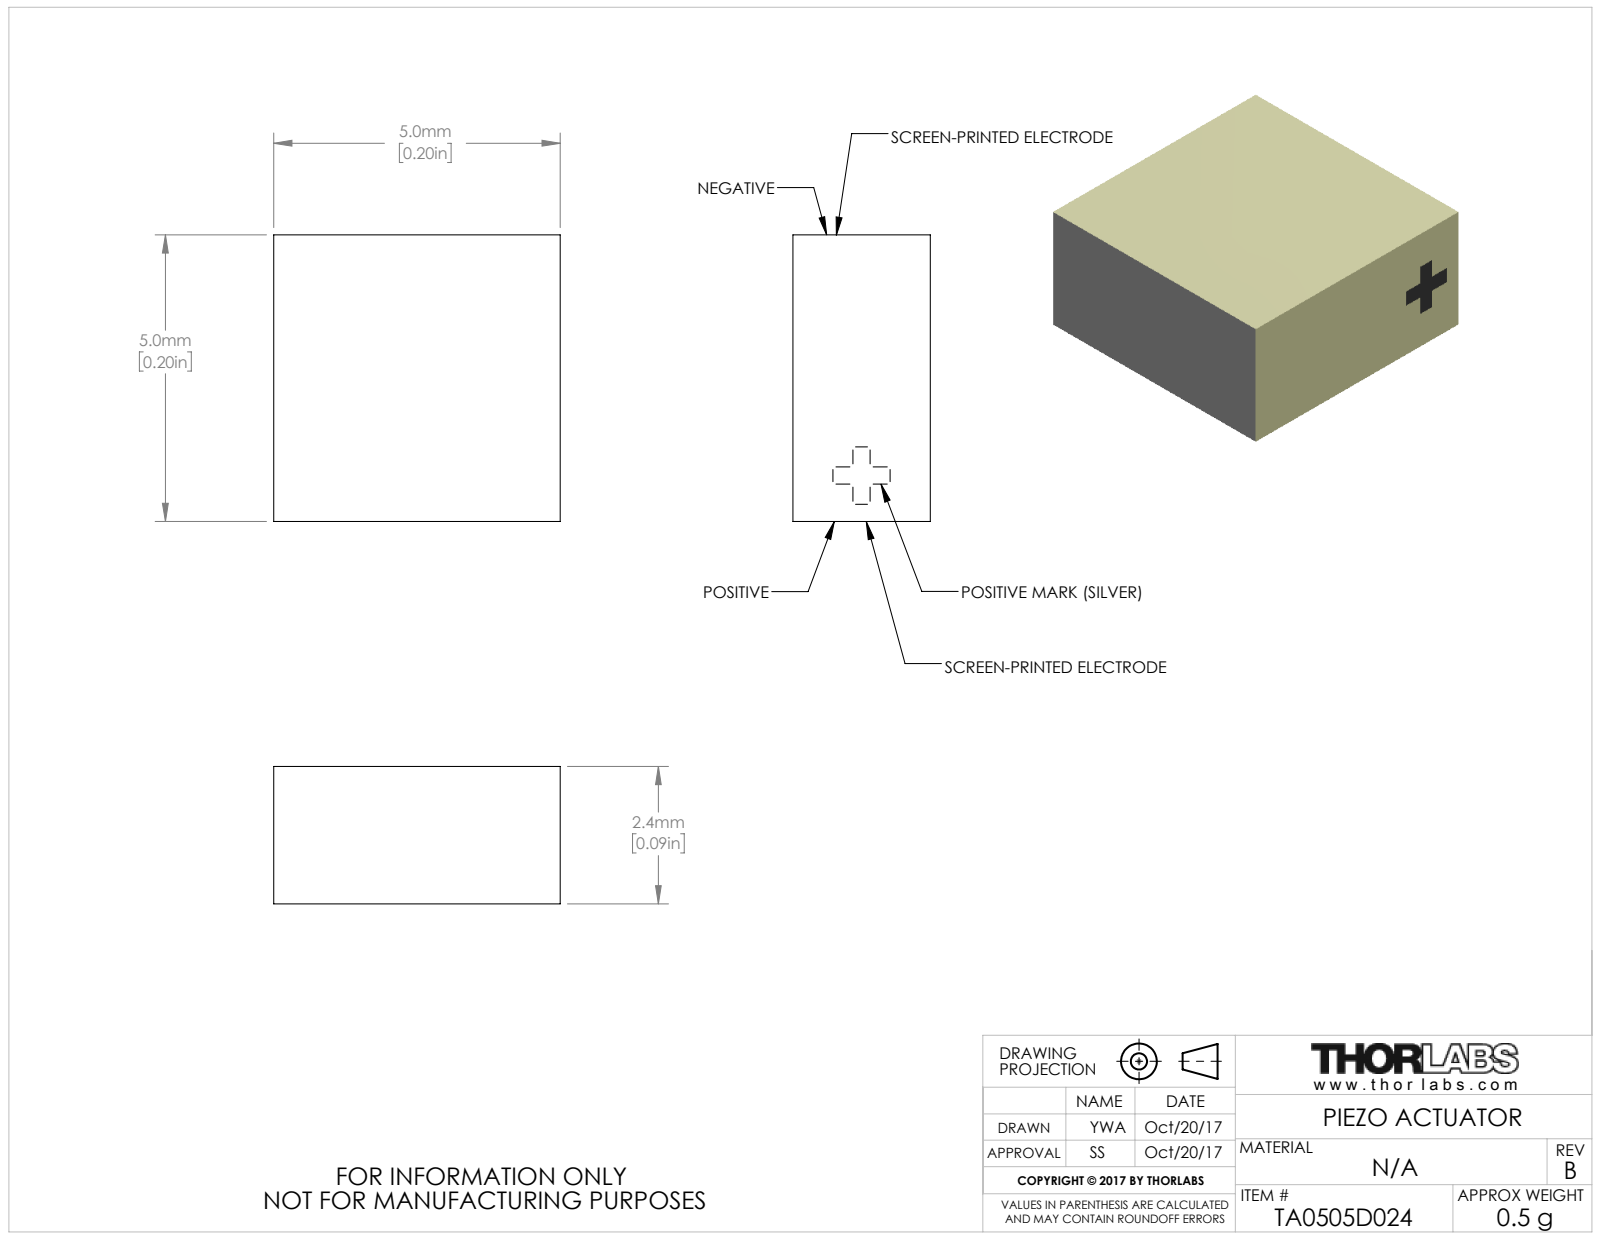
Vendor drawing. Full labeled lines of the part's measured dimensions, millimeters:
Part name (STEP PRODUCT): CTN002214
STEP written by: SolidWorks 2016 (AUTOMOTIVE_DESIGN)
Units: millimetres
Bodies: 1 solid, 7 faces (7 planar, 0 cylindrical, 0 other)
Overall size (bounding box): 5 × 5 × 2.4
Volume: 60 mm³ · Surface area: 98 mm²
Main face-to-face distances: 2.4, 5
